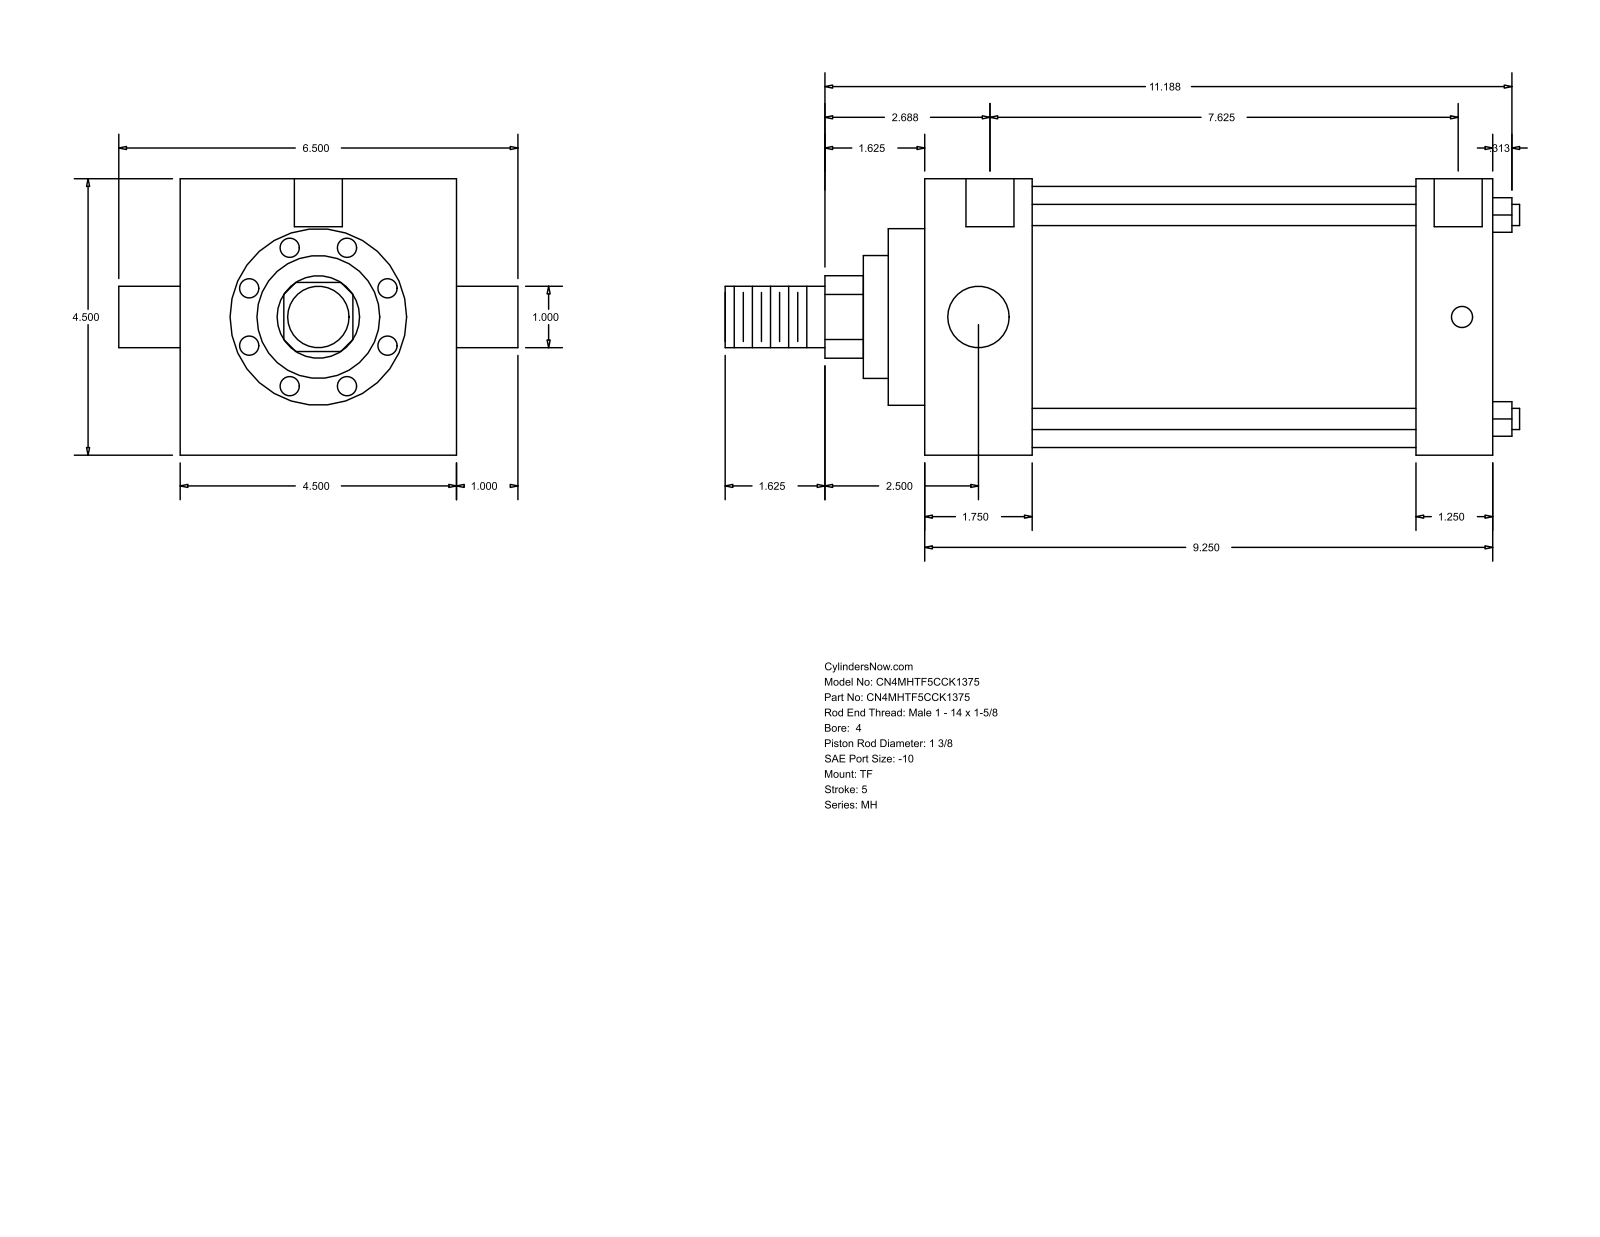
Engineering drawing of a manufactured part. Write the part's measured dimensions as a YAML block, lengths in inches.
part_name: "MH_TF__0400_1.375"
step_written_by: "GSSL Pune (CONFIG_CONTROL_DESIGN)"
units: inches
bodies: {solids: 0, faces: 86, planar: 61, cylindrical: 25, other: 0}
overall_size: [12.937, 6.5, 4.5]
round_holes:
  - {diameter: 0.344, count: 3}
  - {diameter: 0.781, count: 2}
round_bosses_or_shafts:
  - {diameter: 0.345, count: 4}
  - {diameter: 1, count: 2}
  - {diameter: 4.25, count: 1}
  - {diameter: 2.875, count: 1}
  - {diameter: 2, count: 1}
  - {diameter: 1.375, count: 1}
partial_cylinders:
  - {radius: 0.672, count: 1}
face_to_face_distances: [4.5, 9.25, 1.75, 7.5, 8, 6.25, 1.25, 0.594, 2.344, 8.594]
hole_center_spacings: [0.062, 0.063, 7.625, 7.687, 7.688, 7.75]
